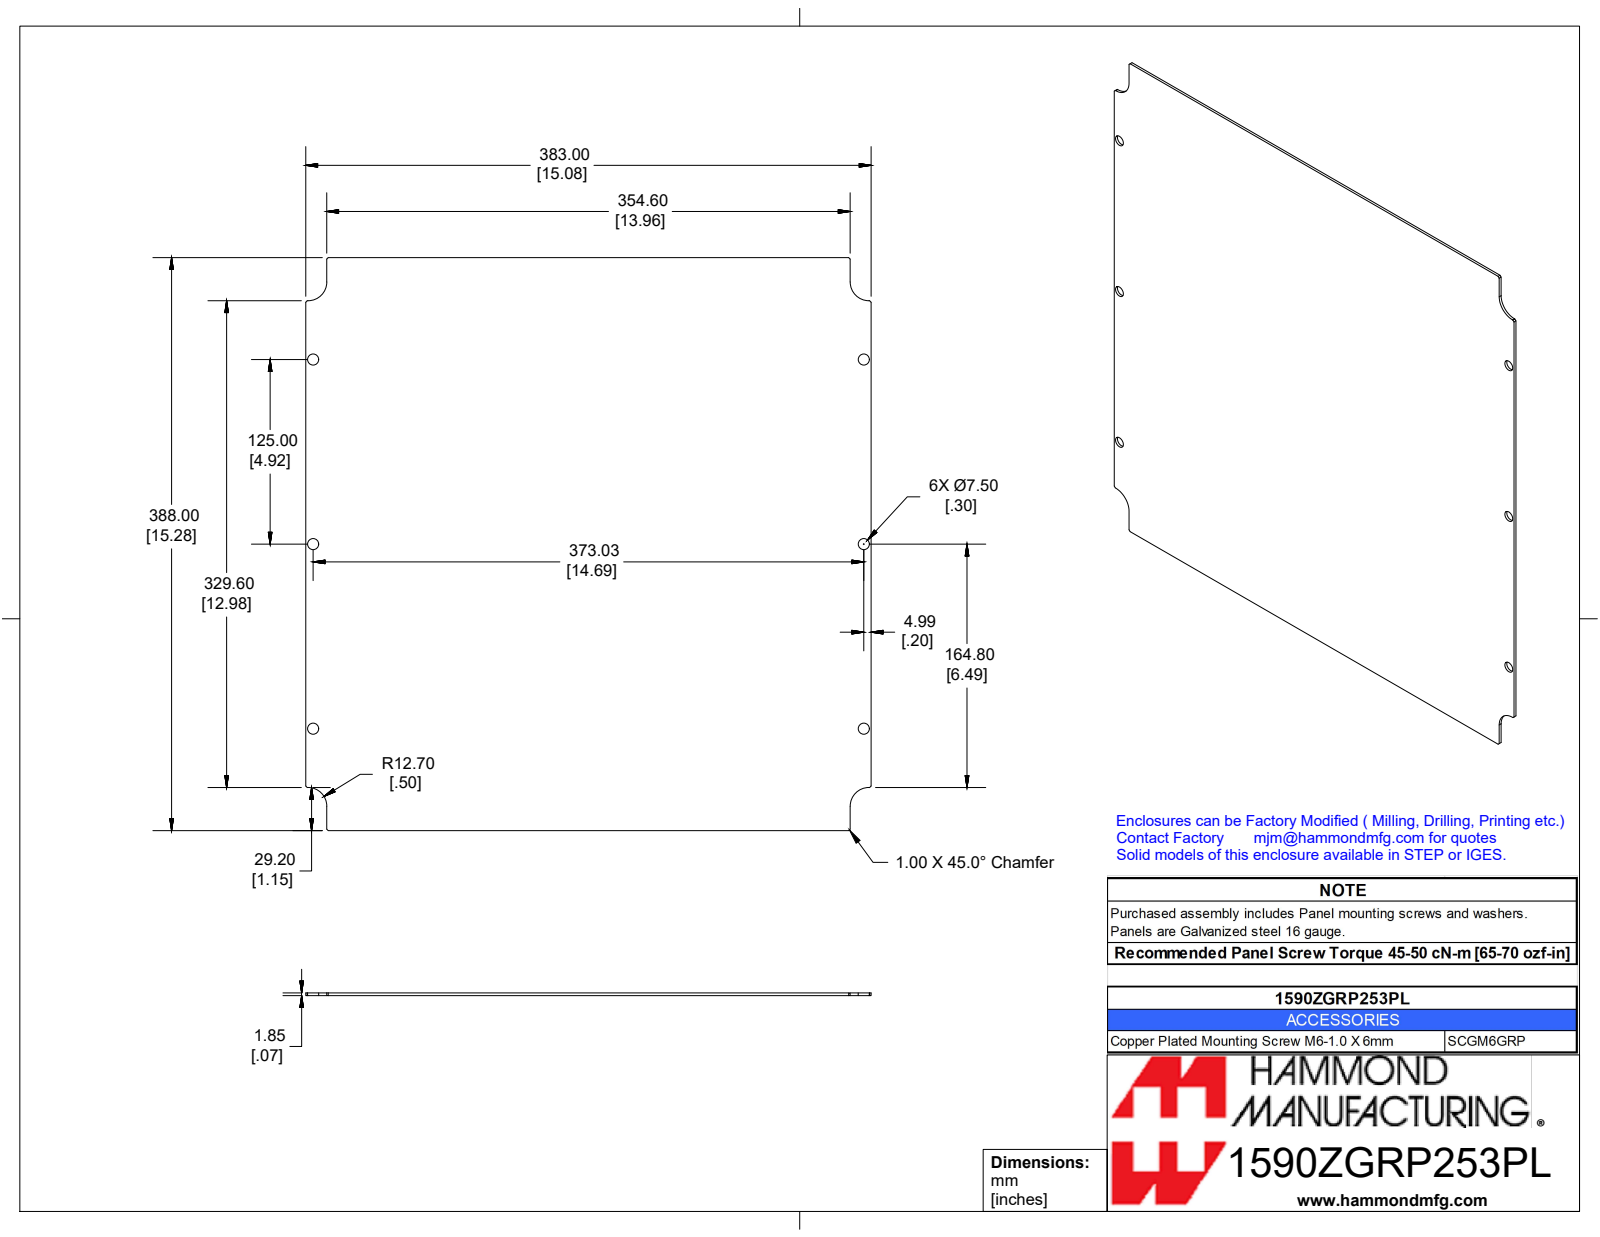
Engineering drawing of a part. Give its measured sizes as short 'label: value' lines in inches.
name: 1590ZGRP253PL
written by: SolidWorks 2019 (CONFIG_CONTROL_DESIGN)
unit: in
bodies: 1 solid, 32 faces (22 planar, 10 cylindrical, 0 other)
size: 15.276 × 15.079 × 0.073
volume: 16.57 in³; area: 459.9 in²
holes: 6× ⌀0.295
rounds: 4× R0.5
face distances: 0.073, 15.276, 15.079, 0.559, 14.52, 13.961, 0.417, 20.197, 20.614, 19.78
hole spacings: 4.921, 15.489, 14.686, 9.843, 17.679
